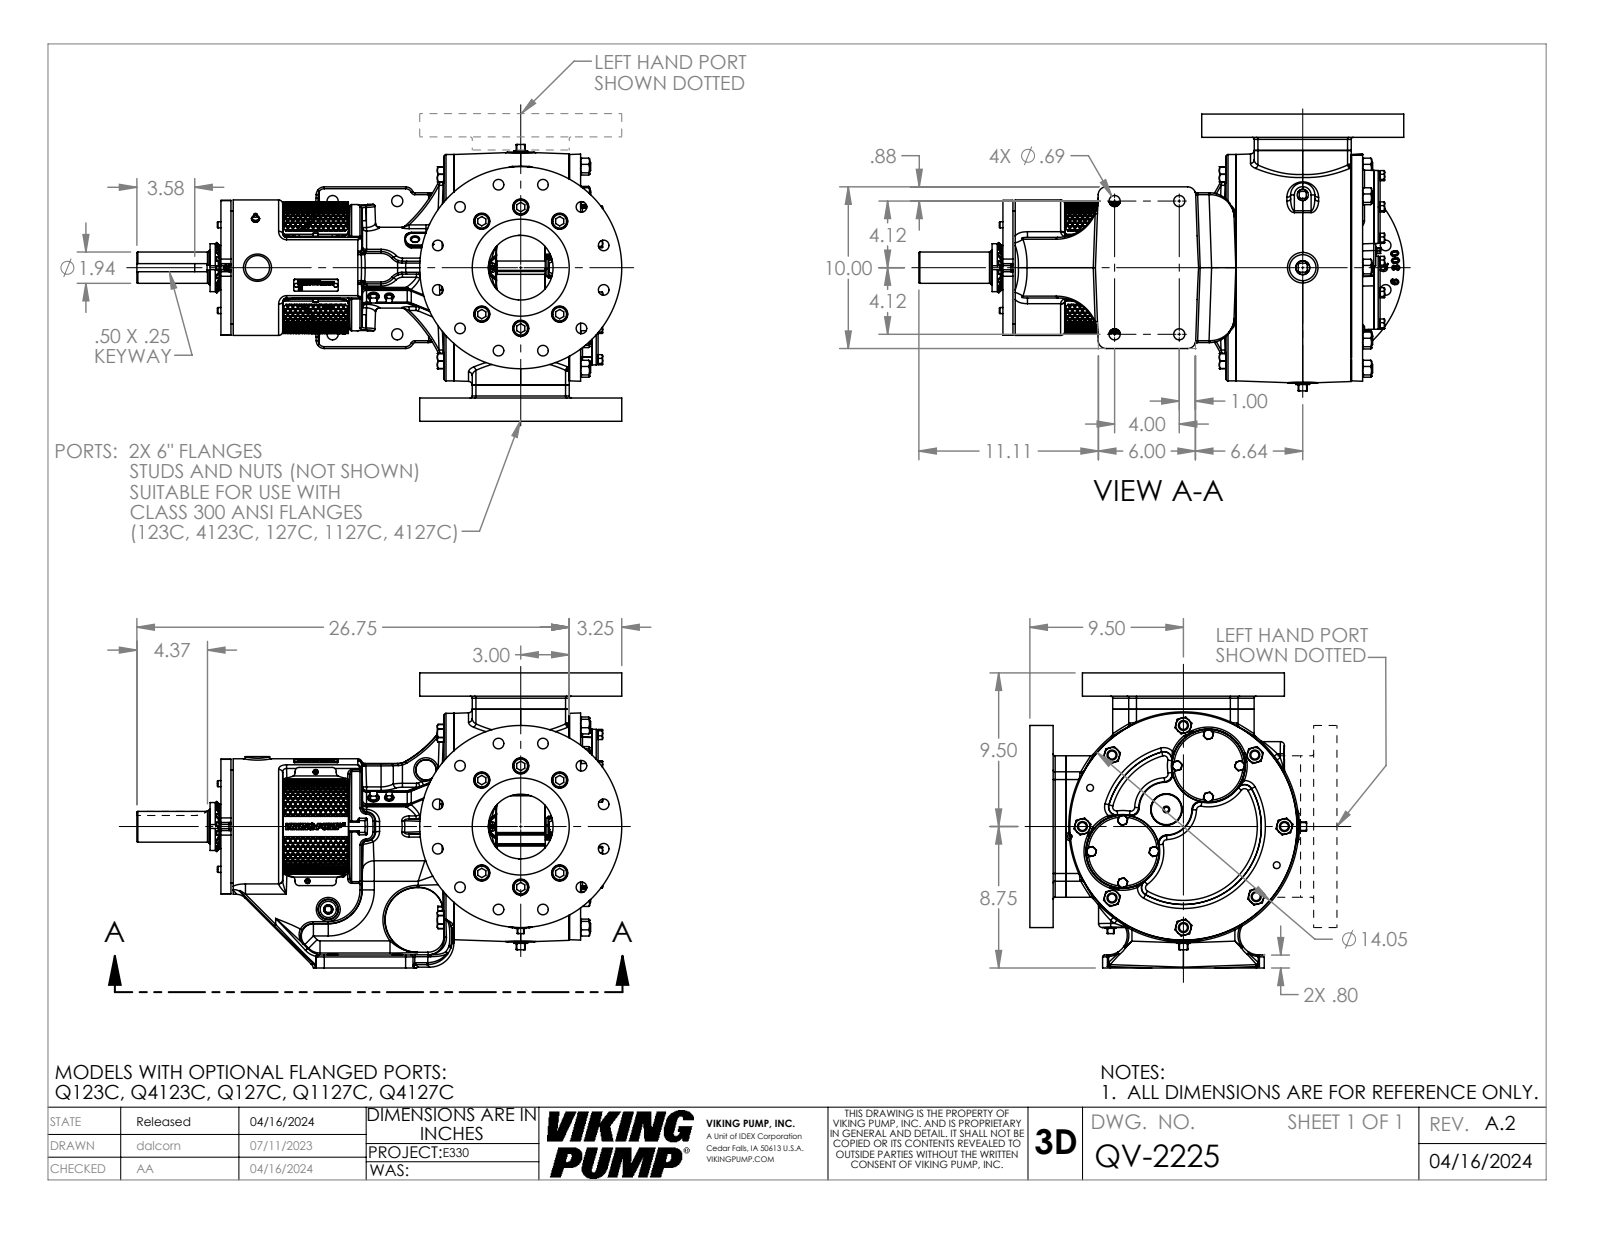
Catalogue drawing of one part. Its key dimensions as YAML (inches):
part_name: "QV-2225"
step_written_by: "SolidWorks 2022 (AUTOMOTIVE_DESIGN)"
units: inches
bodies: {solids: 1, faces: 4218, planar: 1469, cylindrical: 785, other: 1964}
overall_size: [30.001, 18.25, 17.121]
volume: 2303
surface_area: 2532
round_holes:
  - {diameter: 0.656, count: 36}
  - {diameter: 1, count: 12}
  - {diameter: 0.25, count: 9}
  - {diameter: 0.266, count: 8}
  - {diameter: 0.406, count: 8}
  - {diameter: 0.41, count: 8}
  - {diameter: 1.157, count: 8}
  - {diameter: 0.688, count: 4}
  - {diameter: 0.159, count: 2}
  - {diameter: 0.313, count: 2}
  - {diameter: 0.33, count: 2}
  - {diameter: 0.422, count: 2}
round_bosses_or_shafts:
  - {diameter: 0.937, count: 12}
  - {diameter: 0.625, count: 8}
  - {diameter: 0.617, count: 8}
  - {diameter: 0.375, count: 8}
  - {diameter: 0.625, count: 4}
  - {diameter: 0.312, count: 3}
  - {diameter: 0.19, count: 3}
  - {diameter: 12.5, count: 2}
partial_cylinders:
  - {radius: 0.12, count: 60}
  - {radius: 0.25, count: 30}
  - {radius: 0.015, count: 18}
  - {radius: 0.092, count: 18}
  - {radius: 0.07, count: 16}
  - {radius: 0.75, count: 16}
  - {radius: 0.5, count: 15}
  - {radius: 0.06, count: 8}
face_to_face_distances: [1.44, 16.81, 18.25, 3.75, 0.5, 21.756, 22.256, 2.25, 18.006, 18.506]
hole_center_spacings: [5.313, 10.263, 3.75, 2.75, 9.202, 2.079, 7.513, 5.783]
